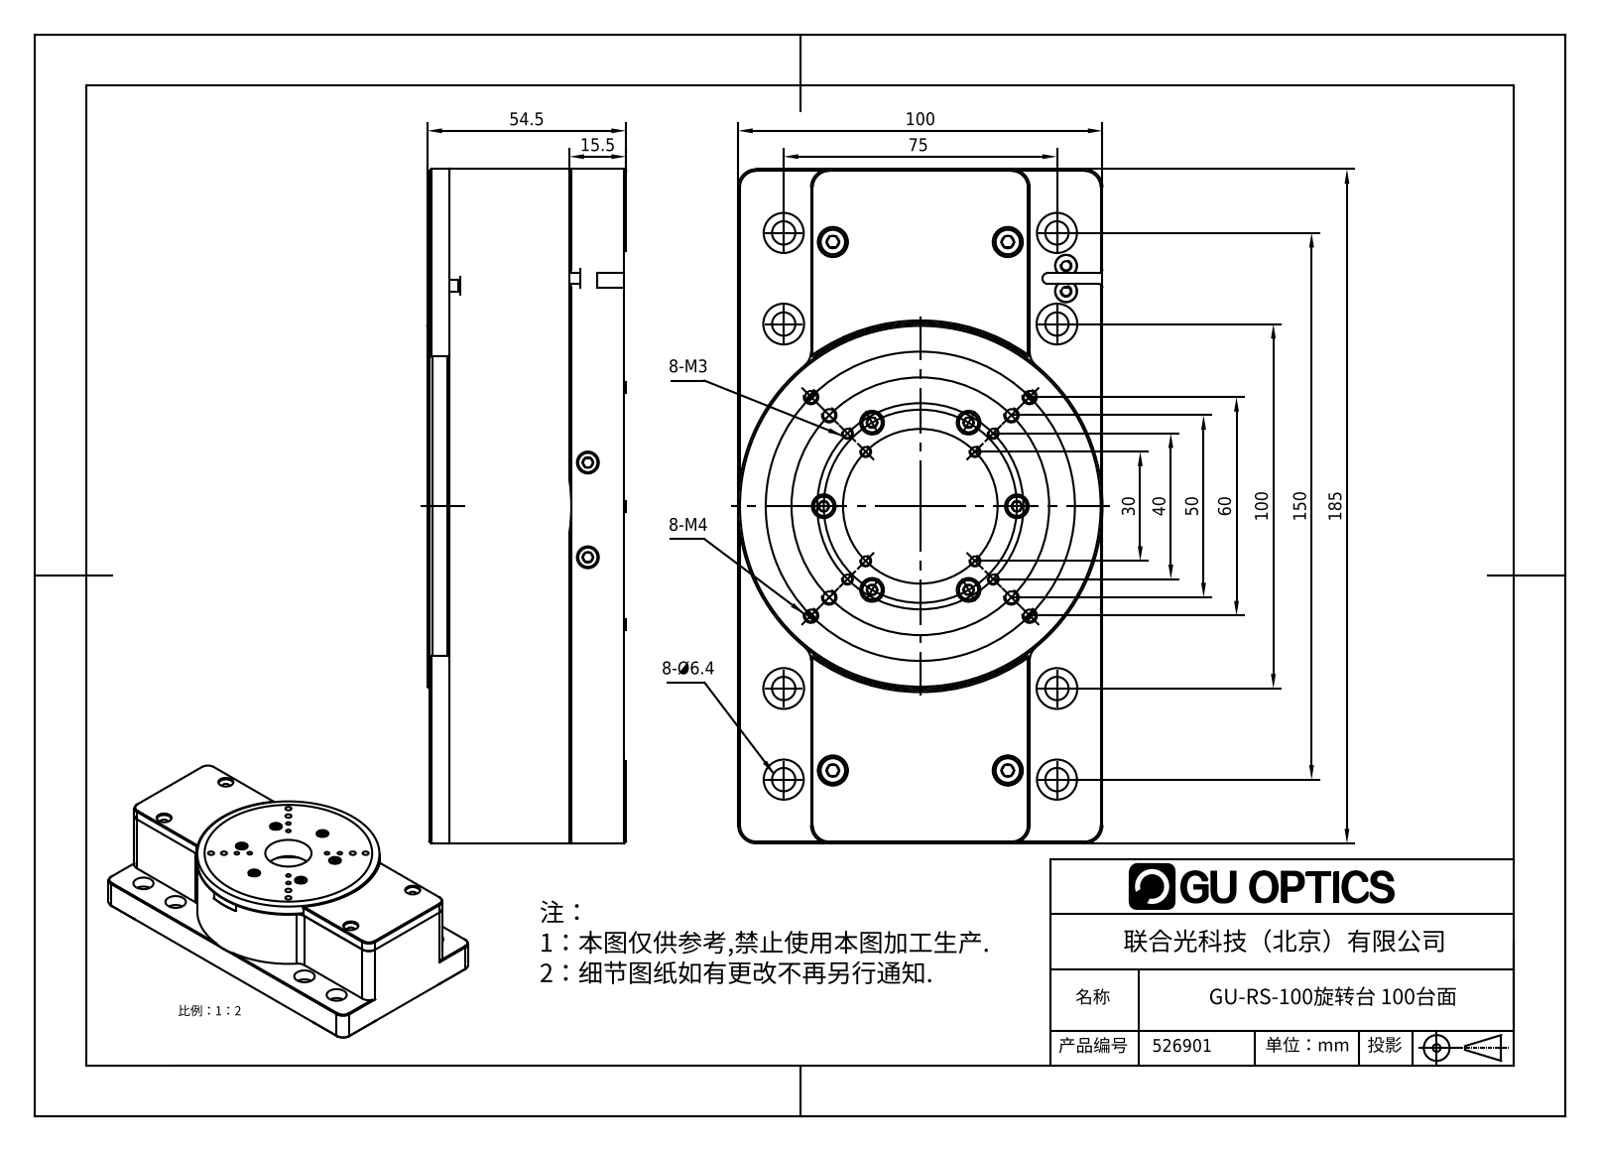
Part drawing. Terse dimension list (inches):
name: GU-RS-100旋转台 100台面
written by: SolidWorks 2016 (CONFIG_CONTROL_DESIGN)
unit: in
bodies: 0 solids, 1393 faces (522 planar, 529 cylindrical, 342 other)
size: 7.283 × 3.937 × 2.146
holes: 40× ⌀0.098, 12× ⌀0.13, 8× ⌀0.252, 6× ⌀0.126, 6× ⌀0.256, 4× ⌀0.081, 4× ⌀0.106, 4× ⌀0.118, 4× ⌀0.157, 4× ⌀0.169, 4× ⌀0.197, 4× ⌀0.325
bosses: 48× ⌀0.118, 8× ⌀0.217, 8× ⌀0.157, 4× ⌀0.128, 4× ⌀0.098, 4× ⌀0.097, 4× ⌀0.097, 1× ⌀3.937
rounds: 30× R0.118, 20× R0.039, 16× R0.197, 4× R0.02, 4× R0.079, 4× R0.11, 3× R0.059, 2× R0.067
face distances: 1.89, 0.079, 0.02, 2.126, 1.811, 0.236, 1.299, 2.047, 0.61, 1.535
hole spacings: 0.278, 1.043, 1.392, 0.557, 0.835, 1.623, 1.783, 1.867
